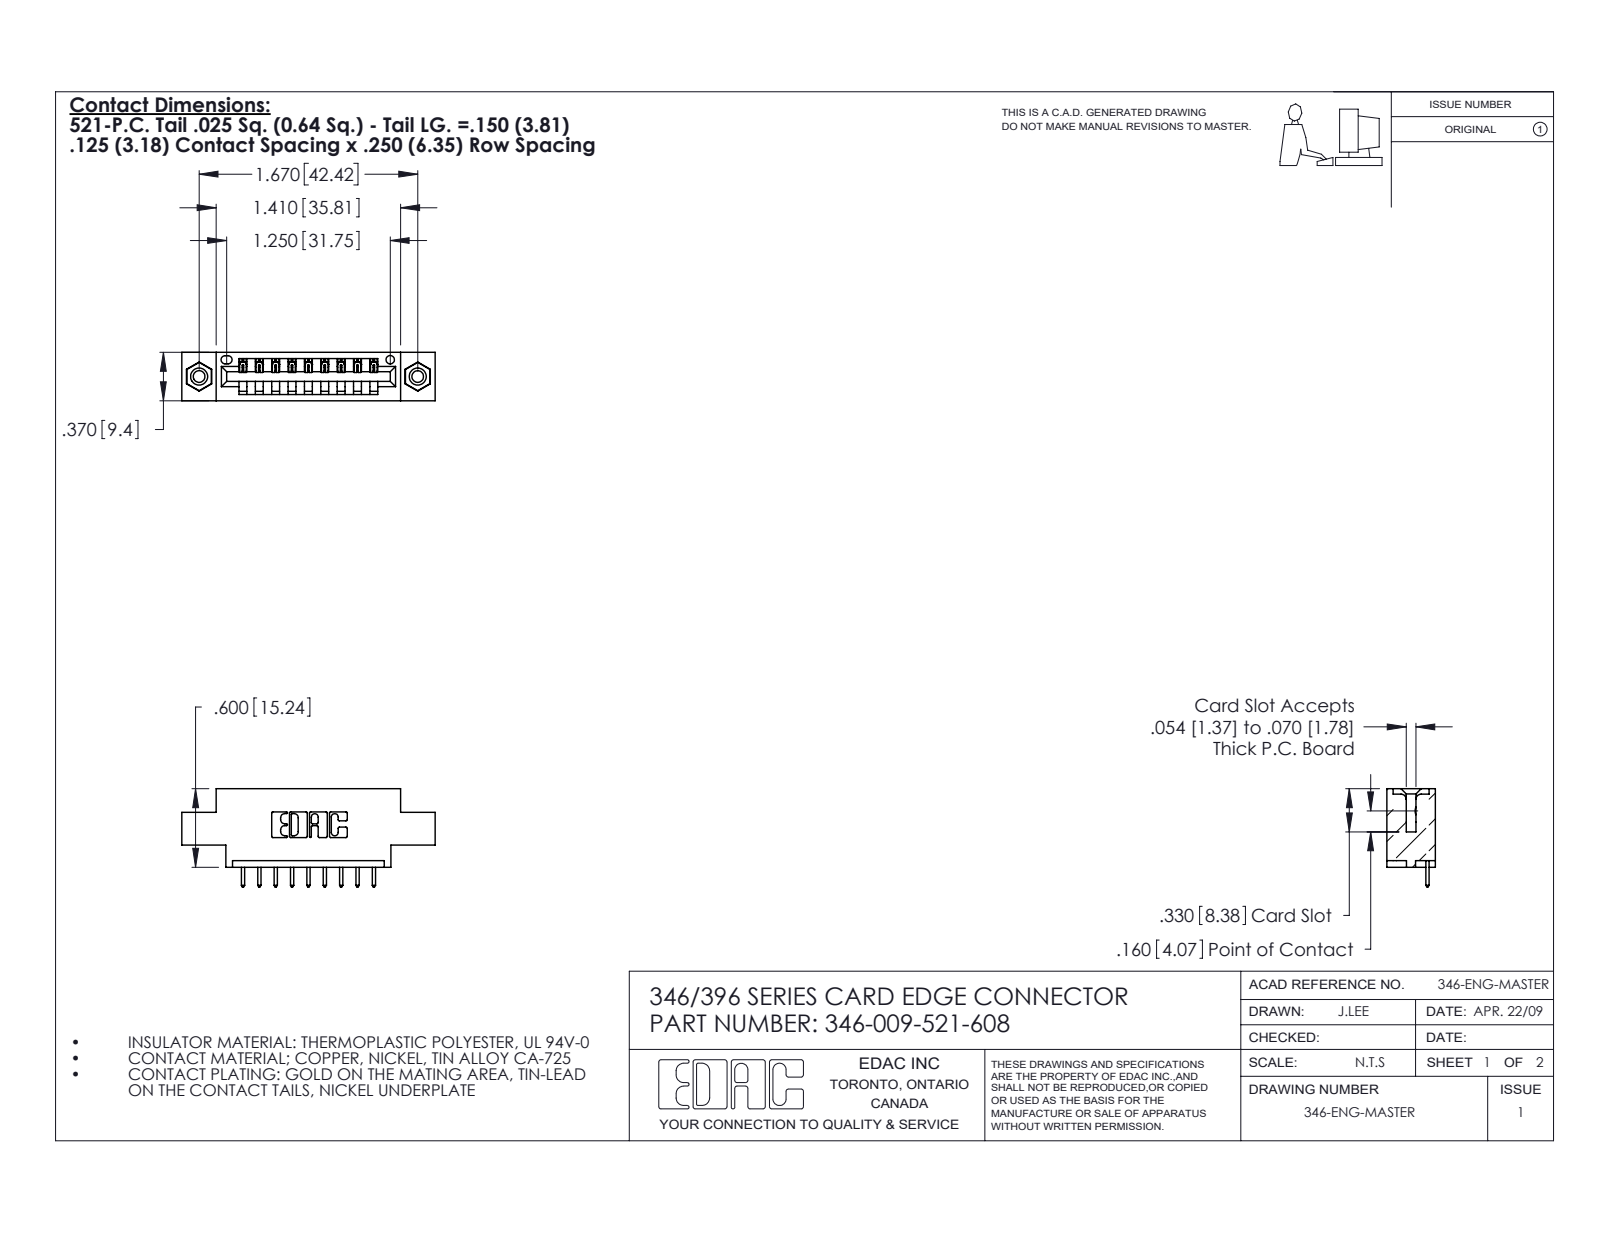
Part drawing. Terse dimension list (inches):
name: 346-009-521-608; 346 Part_0.170 Offset - 0.156 Dia-TI; 345-292-001_345-293-121; 345-250-001_345-250-003-102
written by: SolidWorks 2020 (CONFIG_CONTROL_DESIGN)
unit: in
bodies: 12 solids, 708 faces (472 planar, 220 cylindrical, 16 other)
size: 1.935 × 0.75 × 0.37
volume: 0.262 in³; area: 7.885 in²
holes: 2× ⌀0.089, 2× ⌀0.125, 2× ⌀0.156, 1× ⌀0.064
bosses: 2× ⌀0.155
rounds: 22× R0.01, 18× R0.006, 18× R0.01, 6× R0.007, 6× R0.031, 3× R0.026, 2× R0.031, 2× R0.04
face distances: 0.25, 0.37, 0.048, 0.322, 0.222, 0.148, 0.1, 0.174, 0.072, 0.298
hole spacings: 0.246, 1.465, 1.67
